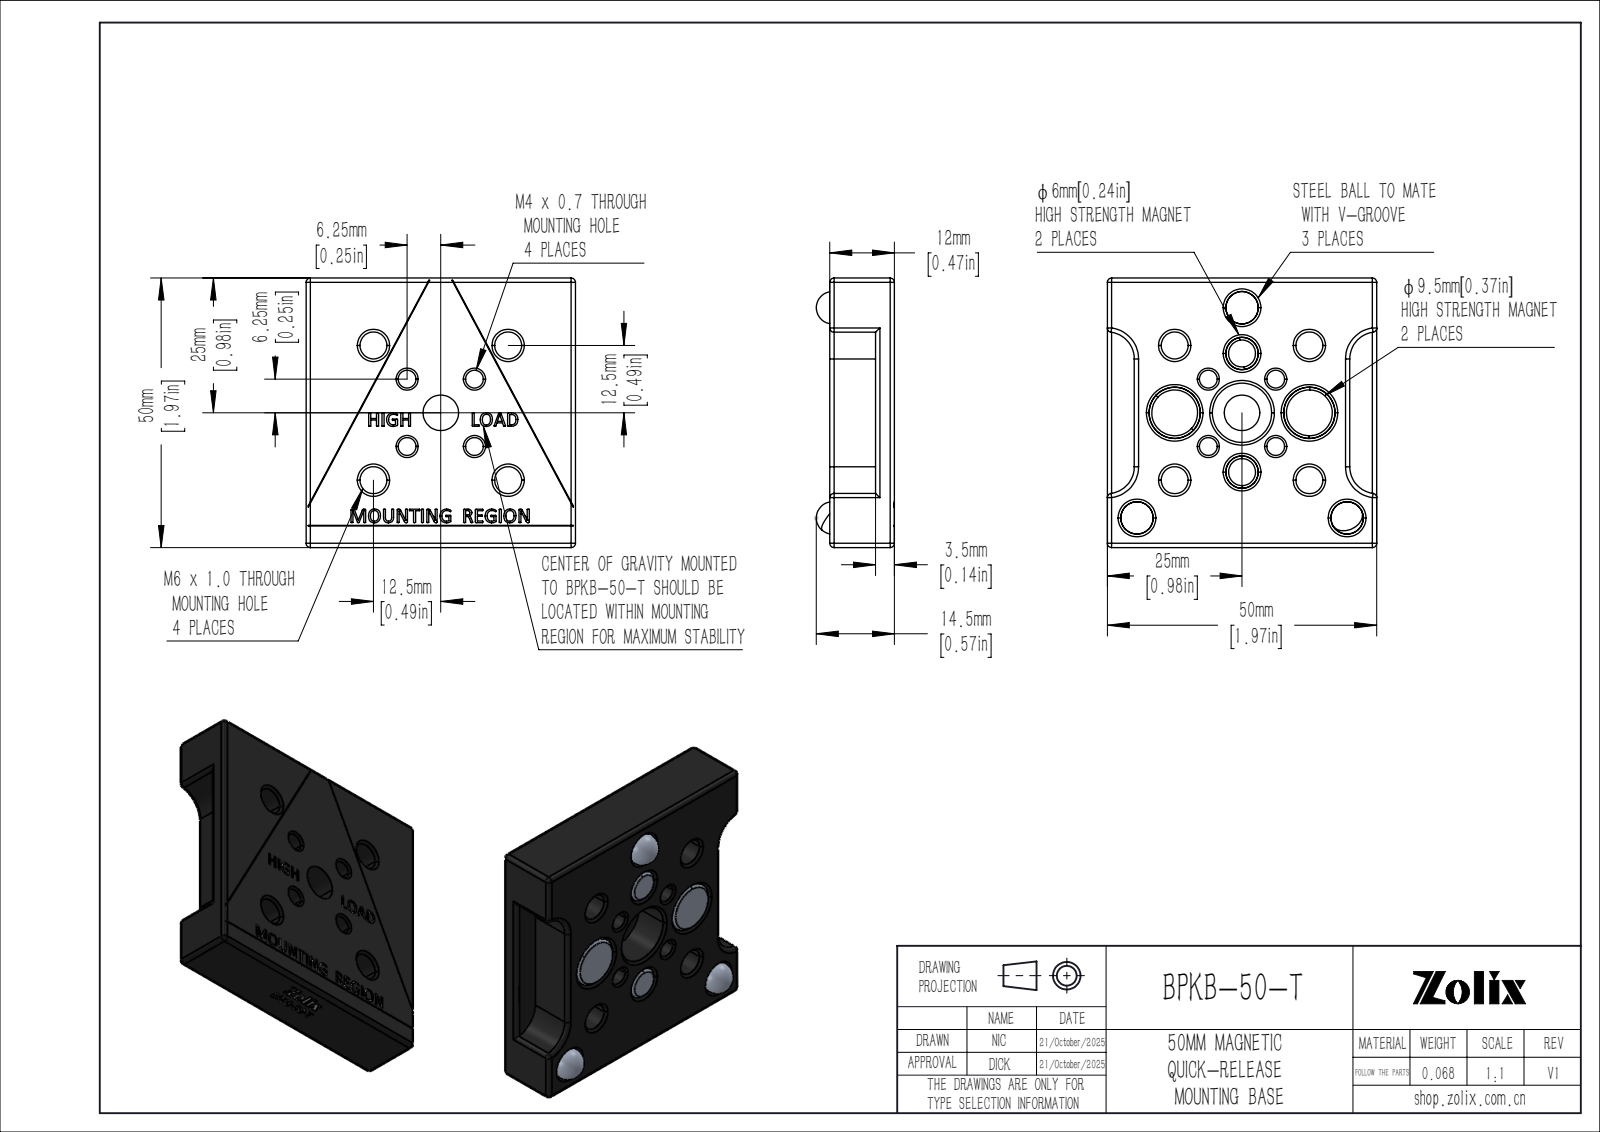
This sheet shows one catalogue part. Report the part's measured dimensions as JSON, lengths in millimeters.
{"part_name": "BPKB-50-T", "step_written_by": "SolidWorks 2020 (CONFIG_CONTROL_DESIGN)", "units": "millimeters", "bodies": {"solids": 8, "faces": 847, "planar": 416, "cylindrical": 76, "other": 355}, "overall_size": [50, 50, 14.5], "volume_mm3": 25265, "surface_area_mm2": 10491, "round_holes": [[6, 5], [3.3, 4], [5, 4], [2, 2], [3, 2], [9.5, 2], [6.6, 1], [11, 1]], "partial_cylinders_radius": [[0.8, 20], [5, 4]], "face_to_face_distances": [12, 50, 2.15, 5, 45, 5.65, 6.35, 3.5, 8.5, 40], "hole_center_spacings": [8.84, 19.76, 12.5, 17.68, 25, 7.85, 12.59, 16.65]}
